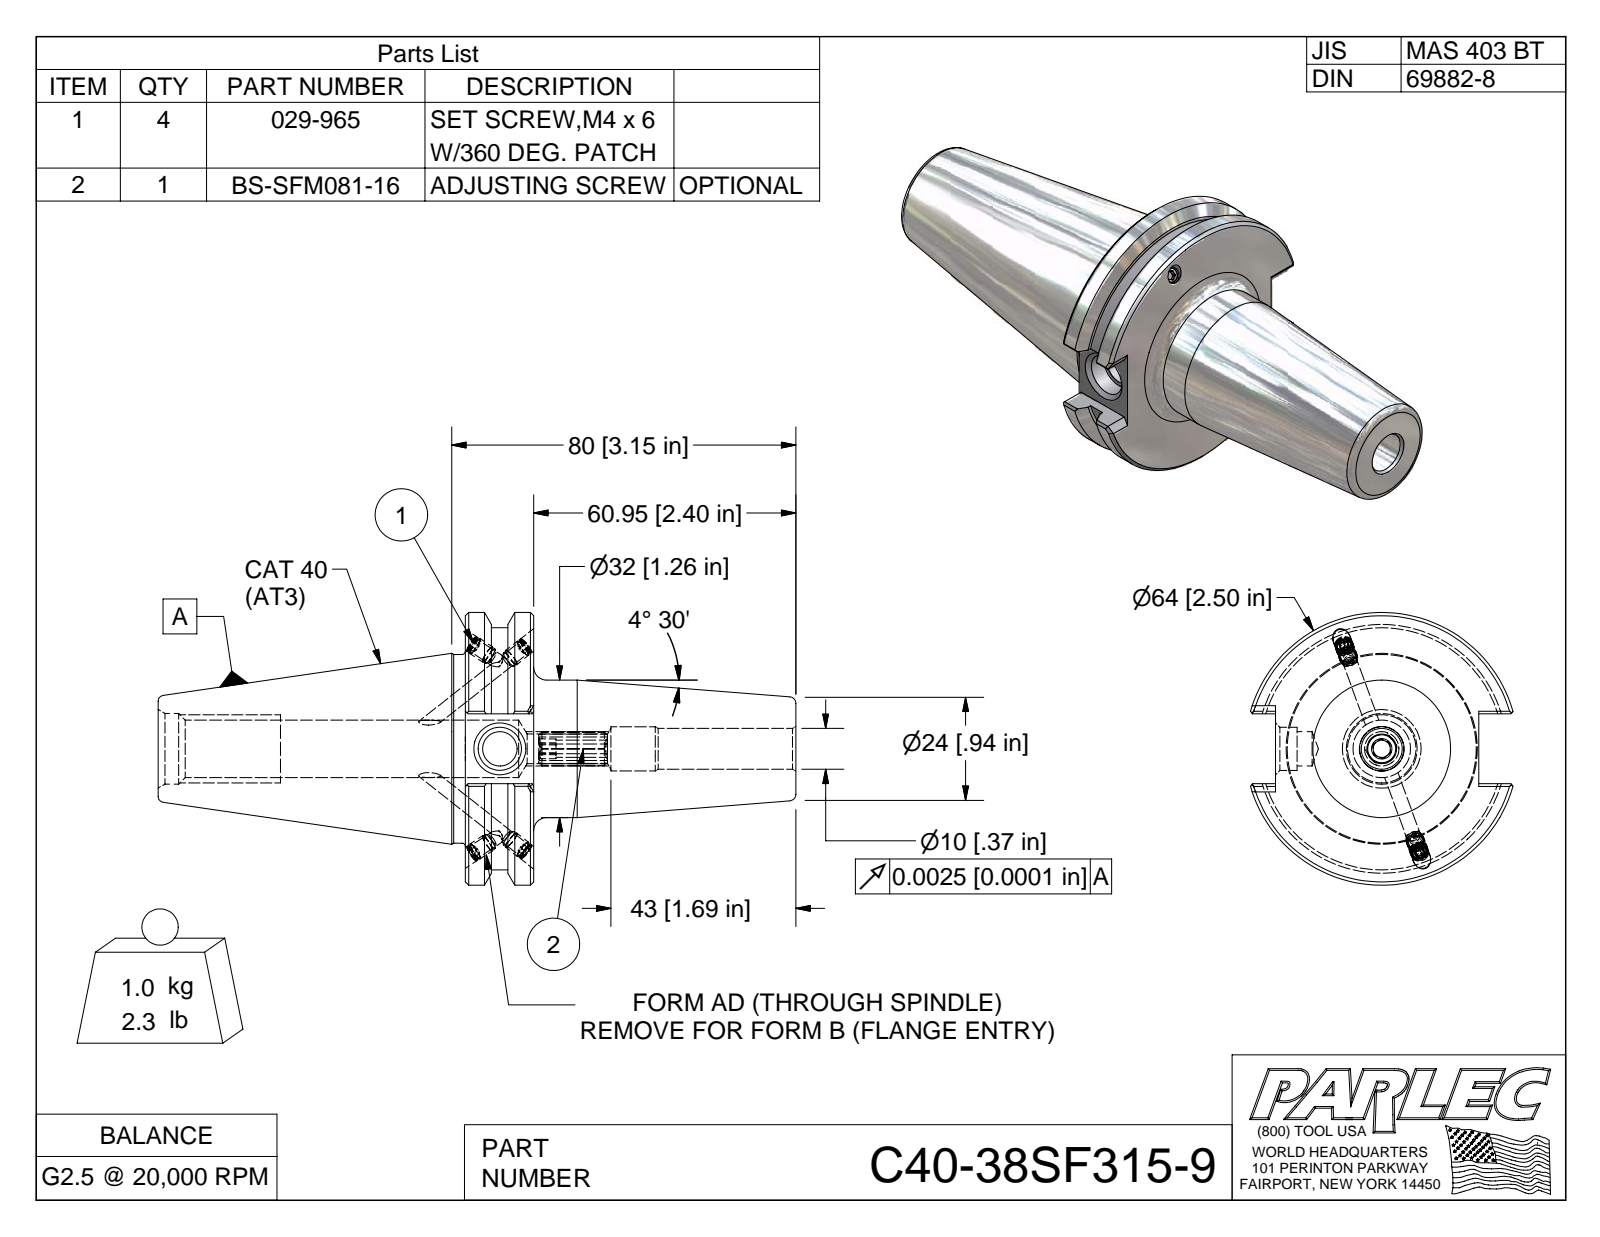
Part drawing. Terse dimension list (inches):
name: C40-38SF315-9; C40BC-38SF315-9-1; 029-965; BS-SFM081-16
written by: Autodesk Inventor 2009 (AUTOMOTIVE_DESIGN)
unit: in
bodies: 6 solids, 172 faces (87 planar, 32 cylindrical, 53 other)
size: 5.837 × 2.5 × 2.403
volume: 8.337 in³; area: 44.69 in²
holes: 4× ⌀0.13, 4× ⌀0.161, 1× ⌀0.374, 1× ⌀0.404
bosses: 4× ⌀0.165, 4× ⌀0.157, 1× ⌀2.5, 1× ⌀2.219, 1× ⌀1.73, 1× ⌀1.26
rounds: 1× R0.157
face distances: 0.625, 3.025, 2.4, 0.64, 1.86, 2.812, 3.437, 5.837, 3.201, 0.389
